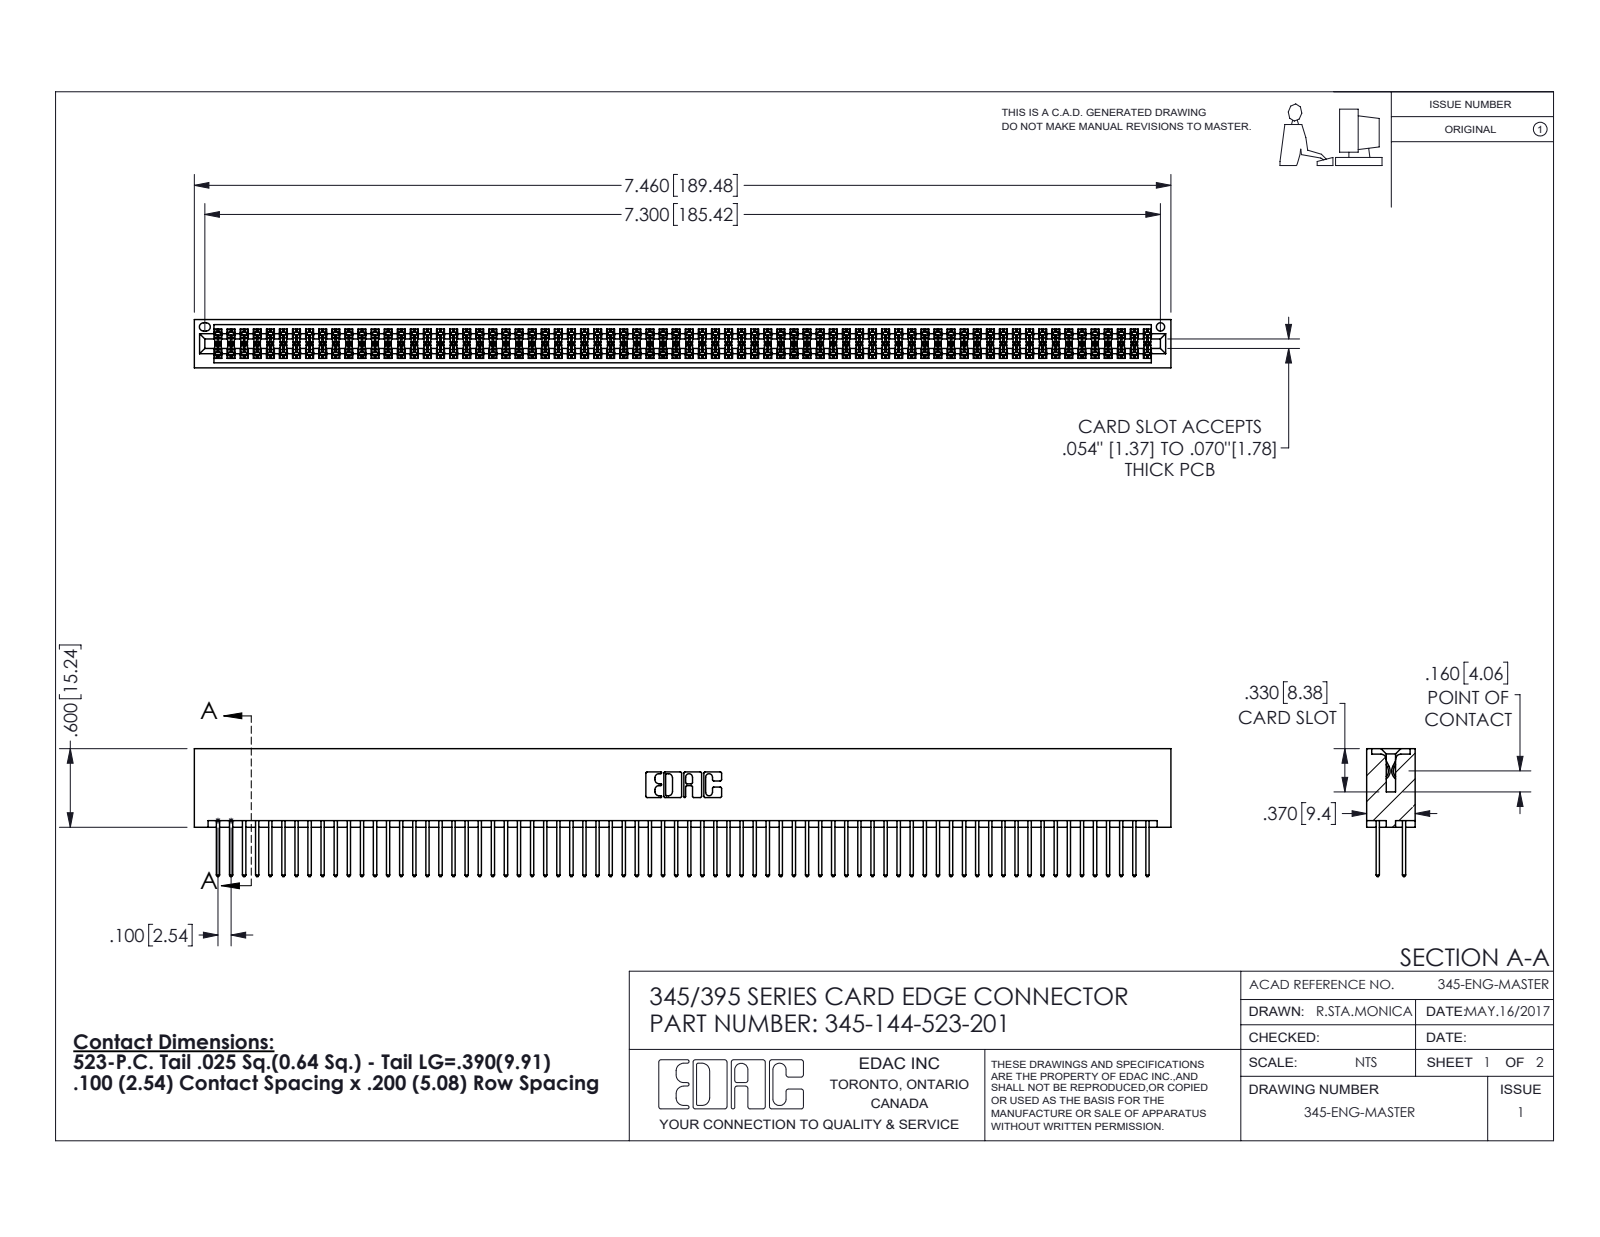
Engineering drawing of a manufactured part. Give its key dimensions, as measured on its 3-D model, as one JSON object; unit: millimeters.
{"part_name": "345-292-001_345-293-123; 345-144-523-201; 345 Part_No Mounting Lugs", "step_written_by": "SolidWorks 2016 (CONFIG_CONTROL_DESIGN)", "units": "millimeters", "bodies": {"solids": 145, "faces": 7318, "planar": 4828, "cylindrical": 2490, "other": 0}, "overall_size": [189.5, 24.8, 9.4], "volume_mm3": 19600, "surface_area_mm2": 31170, "round_holes": [[1.6, 1]], "partial_cylinders_radius": [[0.2, 216], [0.3, 144], [0.3, 22], [0.2, 6], [0.8, 6], [0.7, 3], [0.4, 2], [0.5, 2]], "face_to_face_distances": [7.6, 1.8, 5.1, 2.5, 6.9, 0.6, 9.4, 5.7, 4.4, 3.8]}
